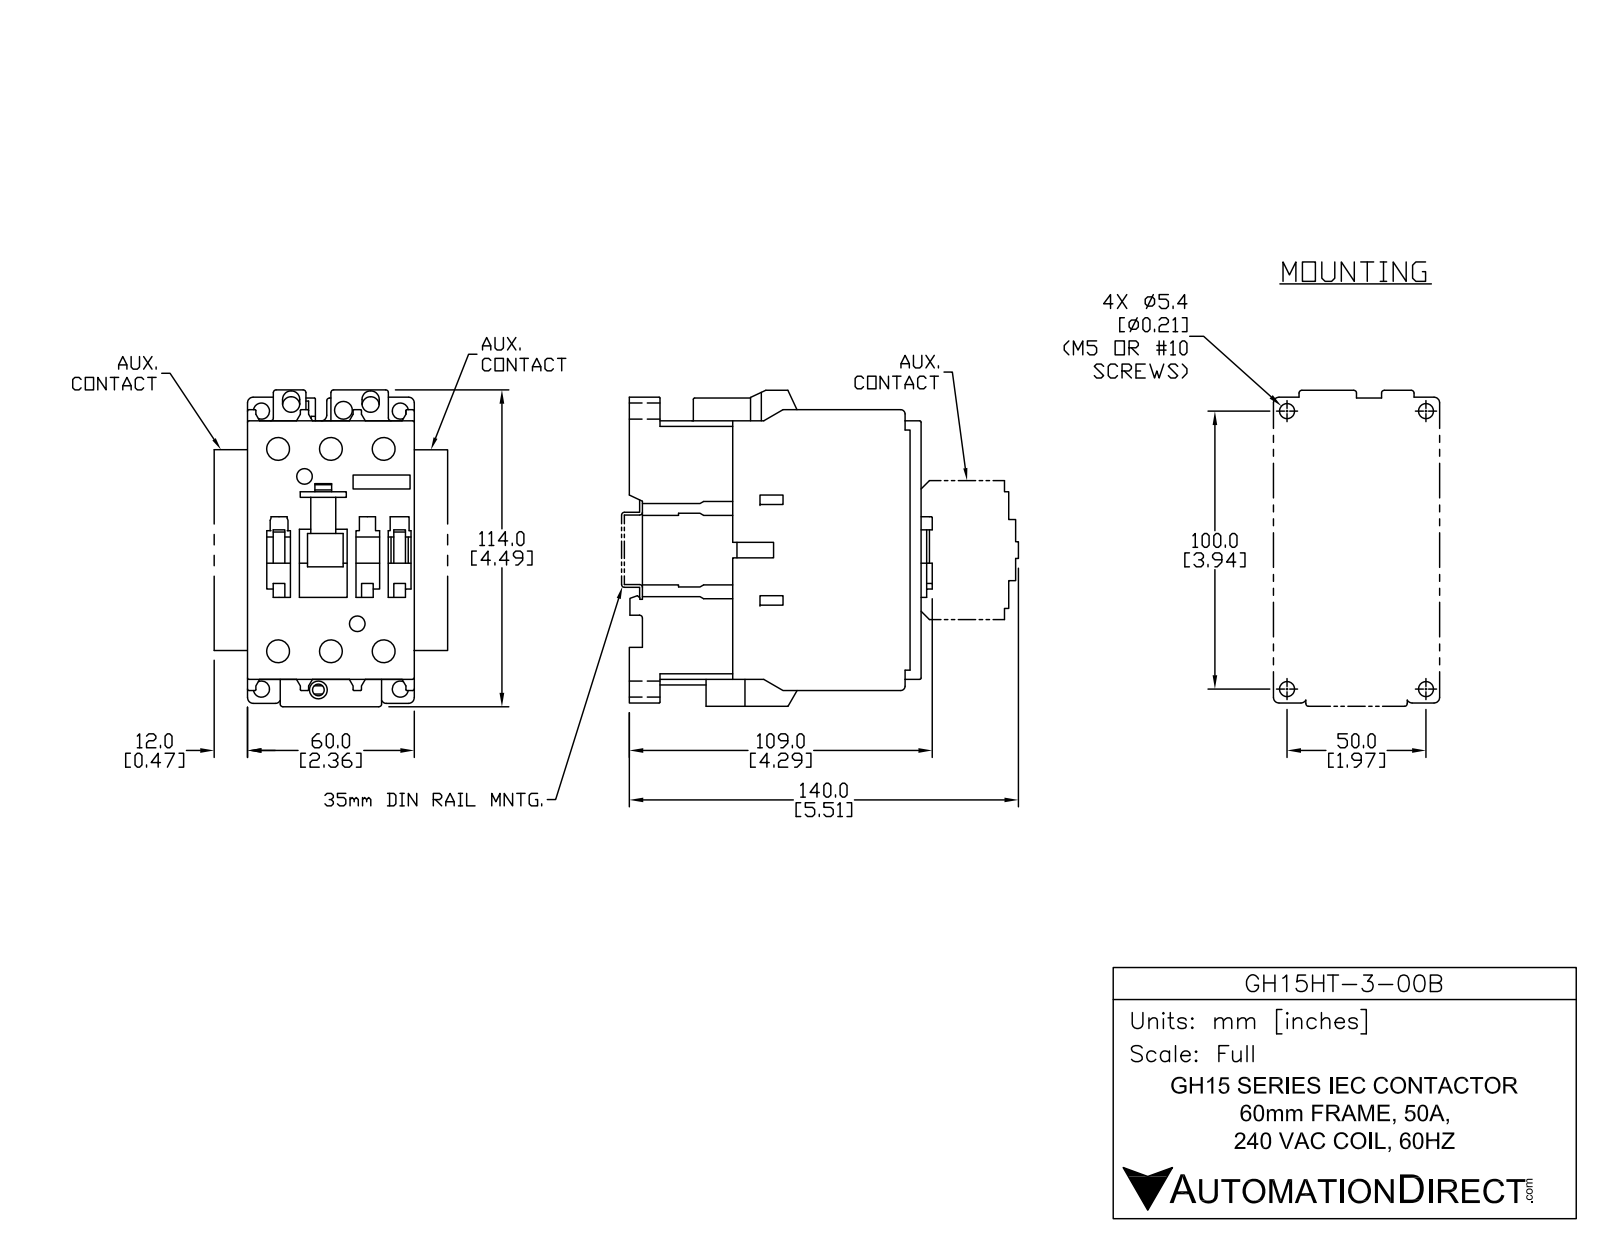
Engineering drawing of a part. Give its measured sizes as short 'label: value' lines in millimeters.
name: GH15HT-3-00B
written by: SolidWorks 2009 (AUTOMOTIVE_DESIGN)
unit: mm
bodies: 1 solid, 840 faces (640 planar, 40 cylindrical, 160 other)
size: 114 × 109.75 × 60
volume: 561 052 mm³; area: 67 816 mm²
holes: 6× ⌀8.5, 4× ⌀6, 1× ⌀5, 1× ⌀6.14, 1× ⌀6.5
rounds: 10× R2, 2× R1.23, 2× R1.25
face distances: 60, 19, 99.5, 93, 10.5, 38, 8.5, 5, 20.5, 67.25
hole spacings: 89.8, 15, 19, 28.53, 46.1, 74.95, 86.46, 96.82
